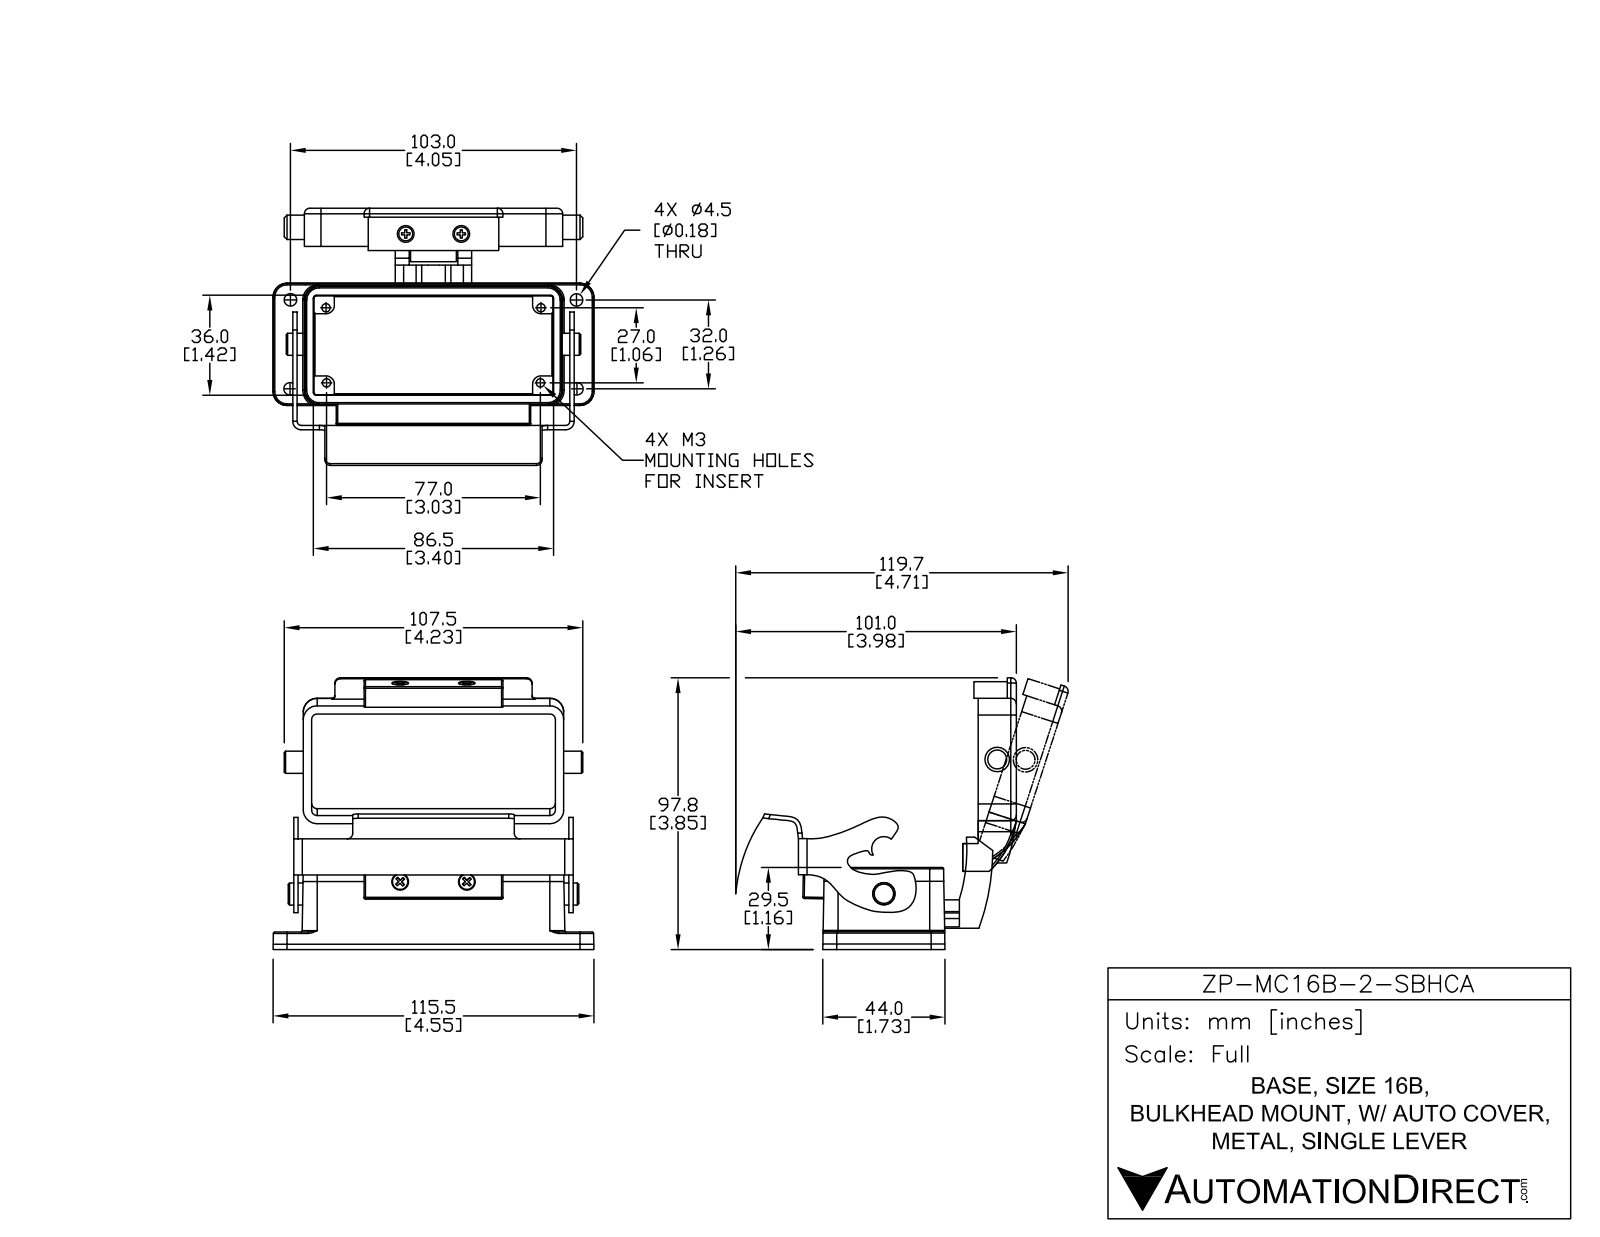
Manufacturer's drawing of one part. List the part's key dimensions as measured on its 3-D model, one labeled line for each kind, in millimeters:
Part name (STEP PRODUCT): ZP-MC16B-2-SBHCA
STEP written by: SolidWorks 2014 (AUTOMOTIVE_DESIGN)
Units: millimetres
Bodies: 3 solids, 428 faces (191 planar, 143 cylindrical, 94 other)
Overall size (bounding box): 115.5 × 97.77 × 86.24
Volume: 83 857 mm³ · Surface area: 50 964 mm²
Round holes (diameter × count): ⌀3 ×4, ⌀4.5 ×4, ⌀2 ×1, ⌀8 ×1
Round bosses / shafts (diameter × count): ⌀8 ×1, ⌀7.95 ×1
Partial cylindrical surfaces — rounded edges, fillets, slot ends (radius × count): R0.5 ×29, R2 ×17, R5 ×6, R2.85 ×4, R3 ×4, R1 ×3, R1.05 ×3, R1.5 ×2
Main face-to-face distances: 3, 1.56, 36, 5.5, 92, 7.06, 93.56, 99.06, 47.52, 49.08
Hole centre spacings: 12.99, 32.14, 90.28, 94.95, 27, 32, 77.5, 82.07
